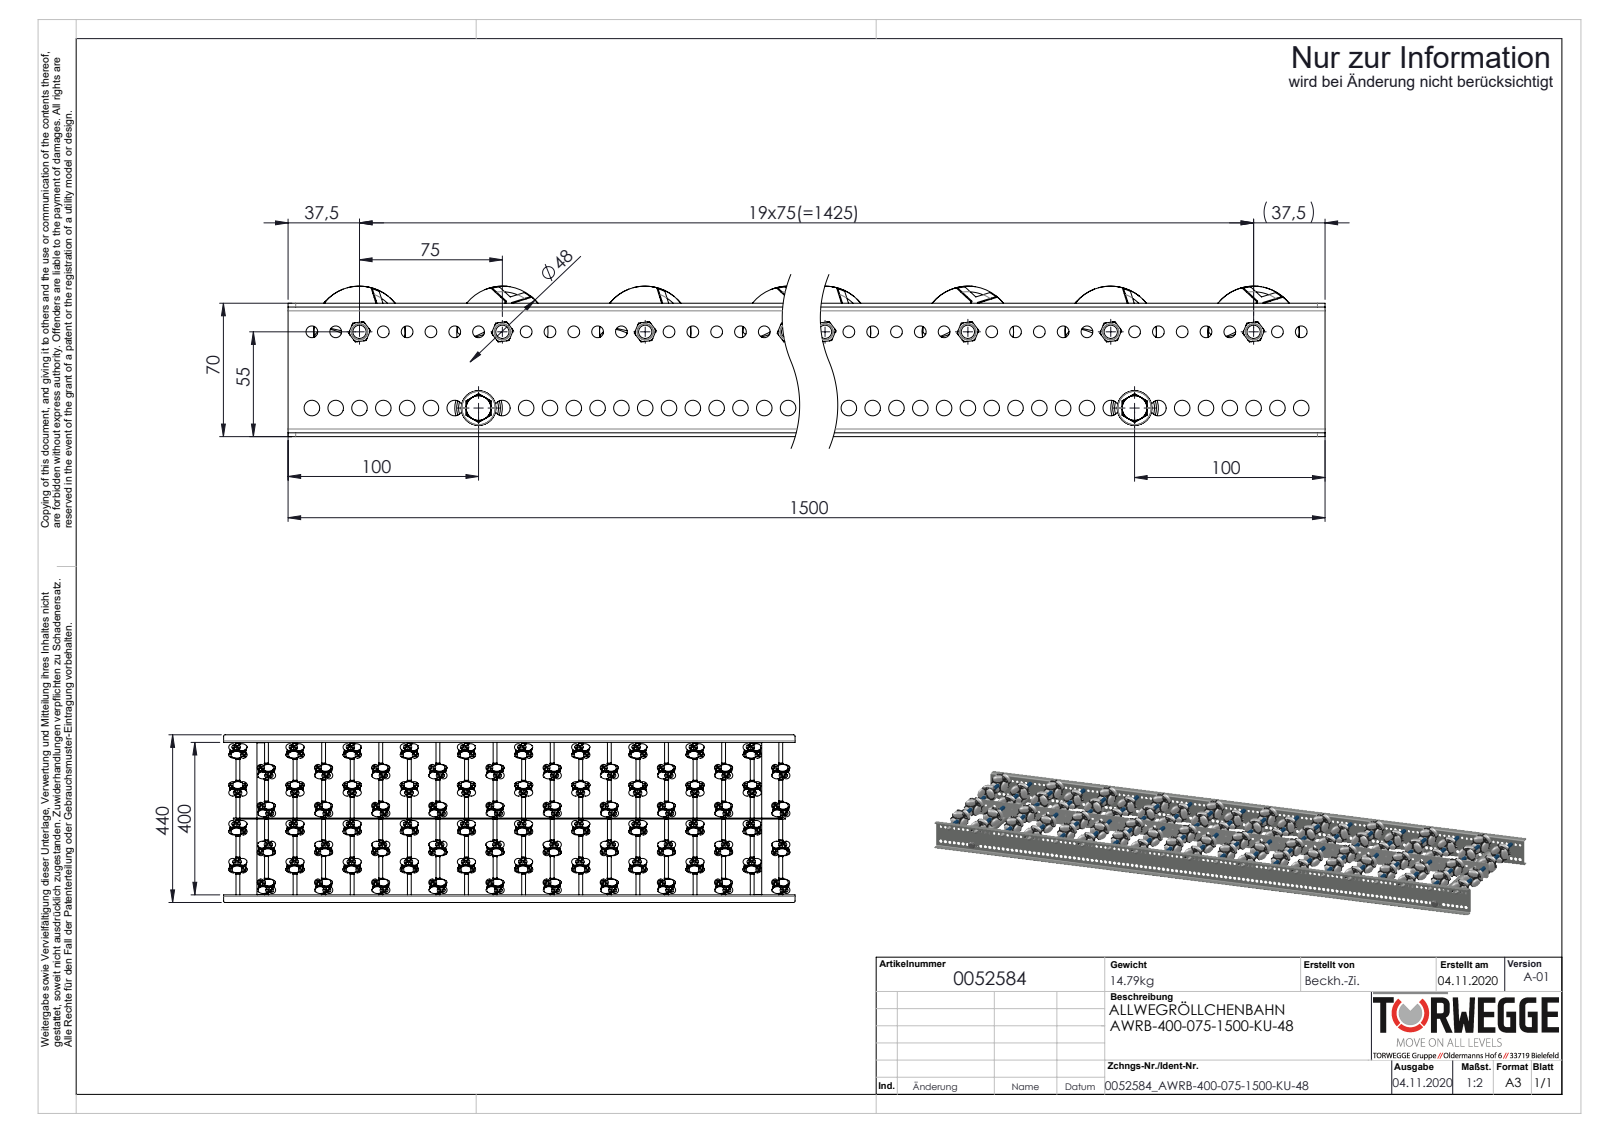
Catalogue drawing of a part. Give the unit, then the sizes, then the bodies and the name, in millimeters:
Units: millimetres
Overall size (bounding box): 1500 × 440 × 79
Round holes (diameter × count): ⌀3.7 ×480, ⌀4.2 ×480, ⌀6.2 ×119, ⌀8.2 ×119, ⌀6.5 ×58, ⌀4.92 ×20, ⌀8.4 ×20, ⌀6.8 ×2, ⌀21 ×2
Round bosses / shafts (diameter × count): ⌀4 ×480, ⌀3.7 ×424, ⌀8 ×22, ⌀42 ×20, ⌀11 ×20, ⌀10 ×20, ⌀7 ×20, ⌀6 ×20
Partial cylindrical surfaces — rounded edges, fillets, slot ends (radius × count): R23.55 ×20, R4 ×8, R2 ×4, R5 ×4
Main face-to-face distances: 2, 402, 68, 400, 404, 203.4, 200.6, 198.6, 201.4, 203.1
Hole centre spacings: 36.06, 36.05, 16.65, 36.04, 33.16, 108.88, 36.07, 143.46
Volume: 4 722 000 mm³ · Surface area: 3 298 000 mm²
Bodies: 1353 solids, 24438 faces (8326 planar, 9648 cylindrical, 6464 other)
Part name (STEP PRODUCT): S108767_Längstraverse-42x2,5-AWR_L1449; 0019719_Gewindestange-M6_L=420; AWR48_Halter; 0027528_BUCHSE-HOHLNIETE ZU AWR48 (+8 more)
STEP written by: SolidWorks 2020 (AUTOMOTIVE_DESIGN)
